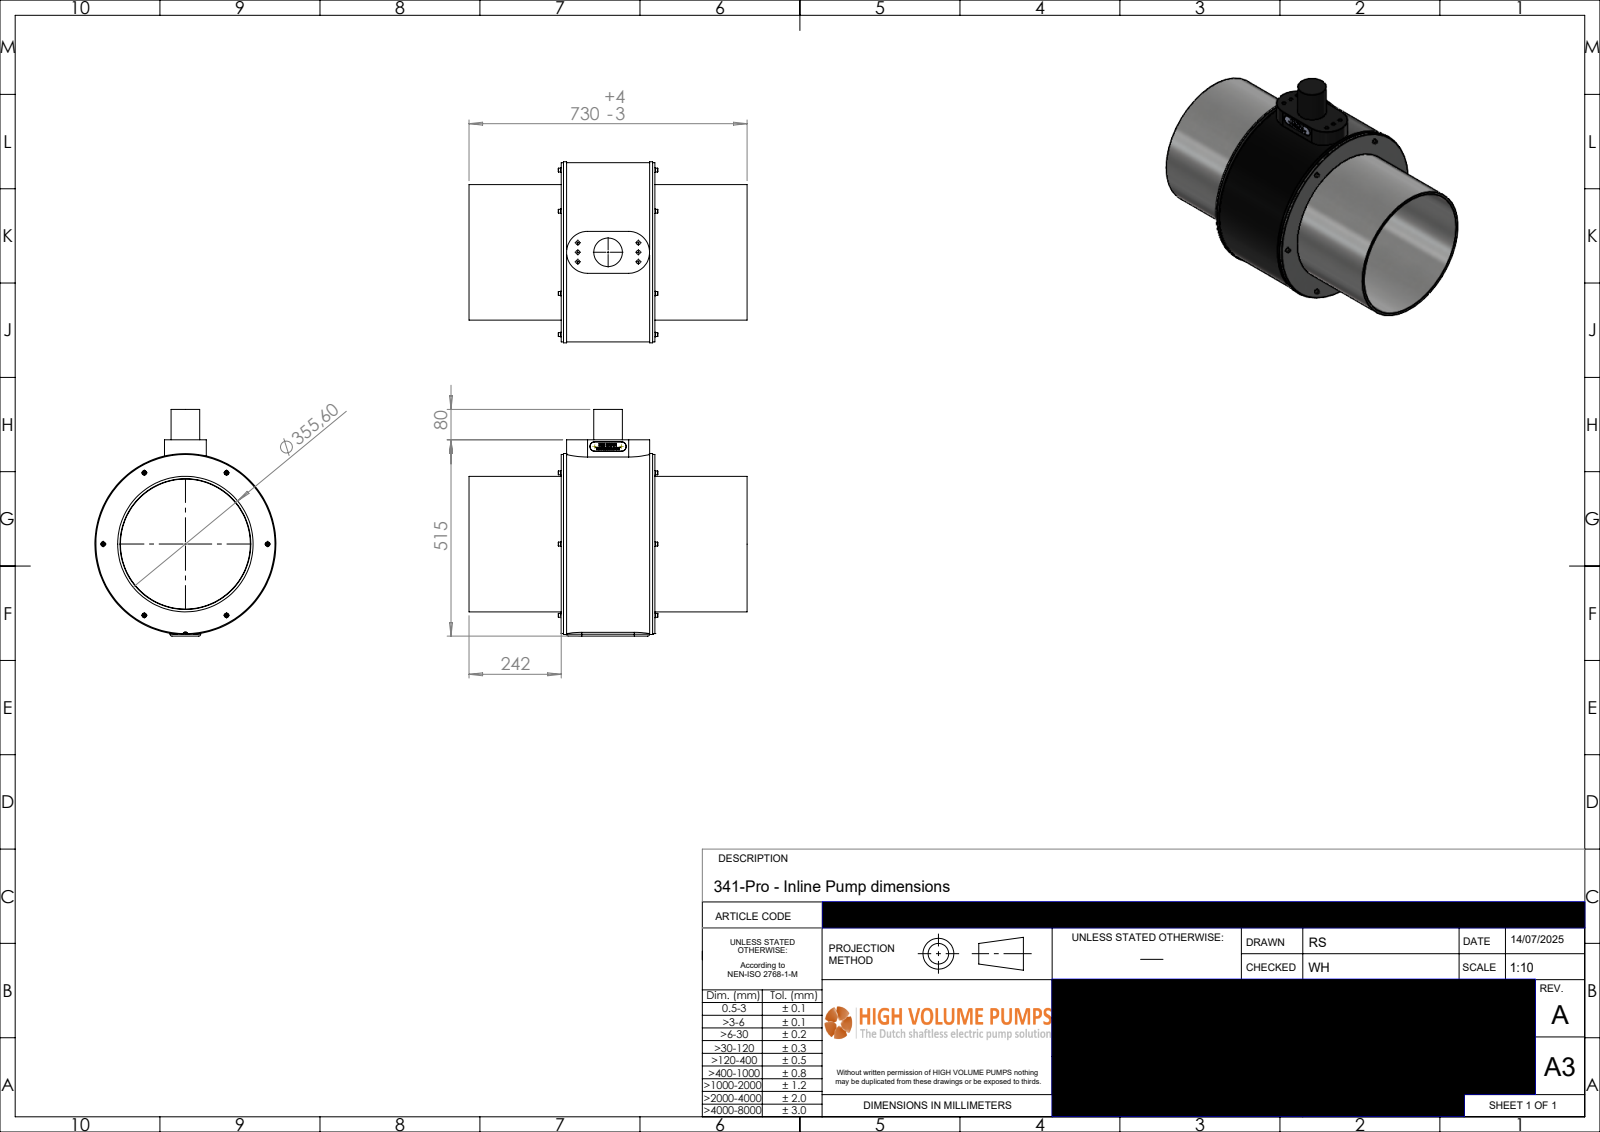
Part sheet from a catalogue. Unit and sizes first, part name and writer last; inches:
Units: inches
Overall size (bounding box): 28.74 × 23.427 × 18.701
Round holes (diameter × count): ⌀0.26 ×6, ⌀0.402 ×6, ⌀13.425 ×1, ⌀13.504 ×1
Round bosses / shafts (diameter × count): ⌀0.472 ×6, ⌀0.456 ×6, ⌀0.394 ×6, ⌀0.236 ×6, ⌀18.701 ×1, ⌀18.504 ×1, ⌀14 ×1, ⌀2.953 ×1
Partial cylindrical surfaces — rounded edges, fillets, slot ends (radius × count): R0.197 ×8, R0.488 ×2, R1.575 ×2, R2.165 ×2
Main face-to-face distances: 9.685, 9.528, 19.213, 20.277, 0.236, 9.764, 18.976, 9.449, 0.551, 10.079
Hole centre spacings: 0.984, 6.337, 6.26, 1.969, 6.562
Volume: 1 521 in³ · Surface area: 2 985 in²
Bodies: 1 solid, 867 faces (601 planar, 88 cylindrical, 178 other)
Part name (STEP PRODUCT): P-341-530-rev-A-IP
STEP written by: SolidWorks 2024 (AUTOMOTIVE_DESIGN)
